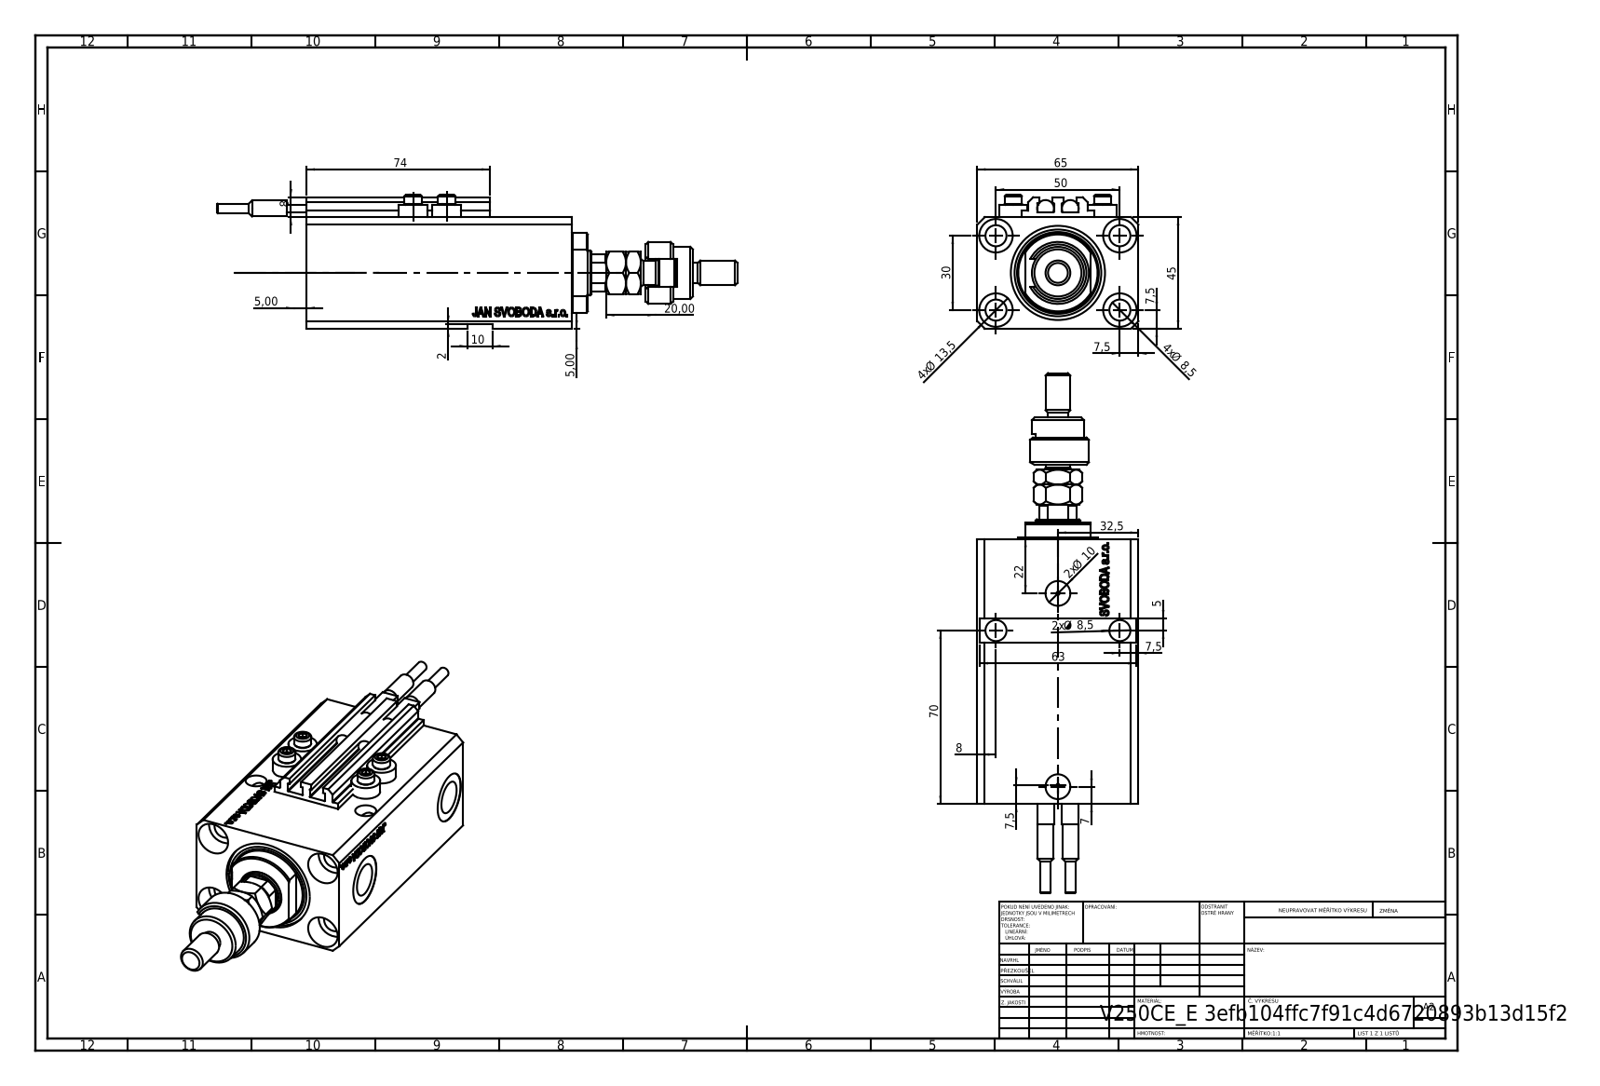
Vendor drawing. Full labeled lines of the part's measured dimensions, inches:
Part name (STEP PRODUCT): MFA; V250CE_VC_E; FEMALE_PART_FOR_DFA; V250CE_C_VCP (+3 more)
STEP written by: SolidWorks 2019 (CONFIG_CONTROL_DESIGN)
Units: inches
Bodies: 12 solids, 1204 faces (571 planar, 151 cylindrical, 482 other)
Overall size (bounding box): 8.264 × 2.559 × 2.126
Volume: 17.83 in³ · Surface area: 133.5 in²
Round holes (diameter × count): ⌀0.335 ×7, ⌀0.049 ×4, ⌀0.157 ×4, ⌀0.531 ×4, ⌀0.394 ×2, ⌀0.518 ×2, ⌀0.787 ×2, ⌀0.709 ×1, ⌀1.496 ×1
Round bosses / shafts (diameter × count): ⌀0.457 ×4, ⌀0.276 ×4, ⌀0.268 ×2, ⌀0.256 ×2, ⌀0.157 ×2, ⌀0.984 ×1, ⌀0.827 ×1, ⌀0.63 ×1
Partial cylindrical surfaces — rounded edges, fillets, slot ends (radius × count): R0.008 ×10, R0.217 ×1, R0.335 ×1, R0.344 ×1, R0.63 ×1
Main face-to-face distances: 1.772, 2.559, 0.079, 3.224, 1.85, 0.118, 0.988, 4.213, 2.953, 0.394
Hole centre spacings: 1.148, 1.969, 0.535, 0.595, 1.098, 1.181, 1.324, 1.417
